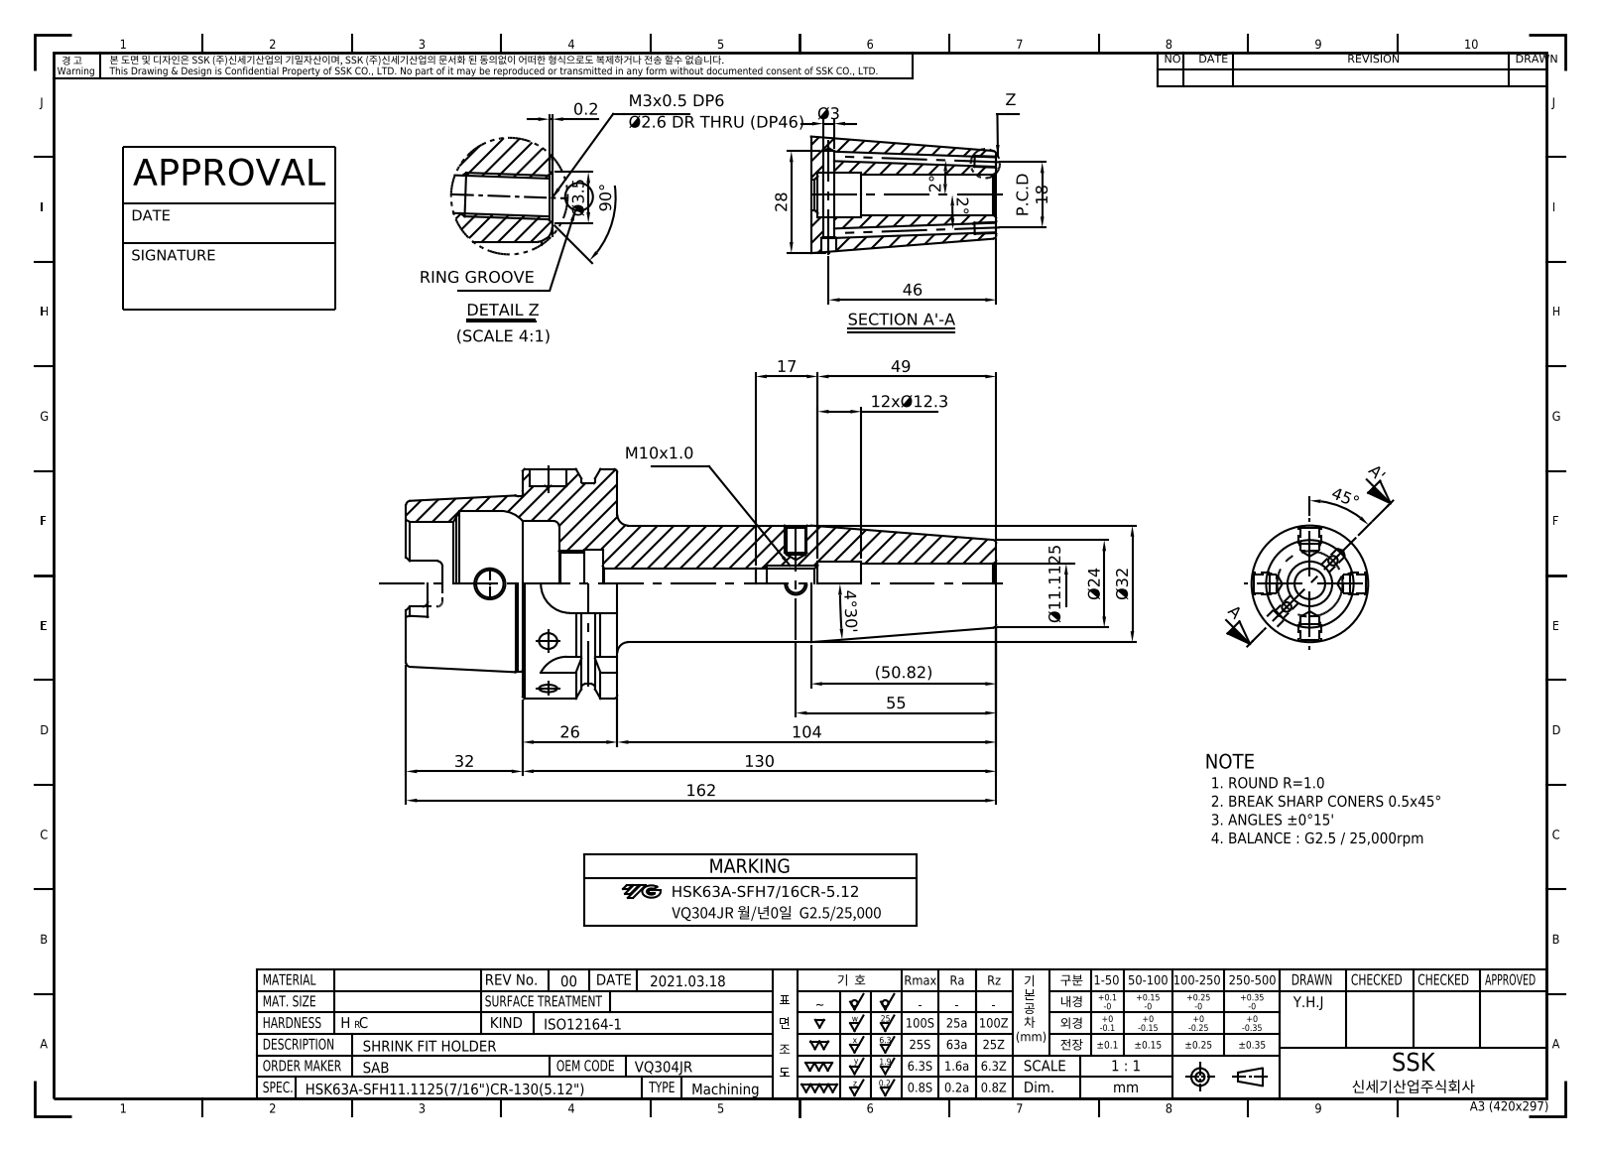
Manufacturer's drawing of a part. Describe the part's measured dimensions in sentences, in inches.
The part is named "LO-HSK63A-SFH11.1125CR-130". Its 3-D file was written by "Autodesk Inventor 2022 (AUTOMOTIVE_DESIGN)". It is 1 solid with 121 faces: 42 planar, 36 cylindrical and 43 other. Overall it measures 6.378 by 2.48 by 2.48 inches. Its volume is 8.988 cubic inches and its surface area 55.14 square inches. Round holes: 2 of diameter 0.097, 1 of diameter 0.295, 1 of diameter 0.331, 1 of diameter 0.351, 1 of diameter 0.394, 1 of diameter 0.437, 1 of diameter 0.484, 1 of diameter 0.666, 1 of diameter 0.748, 1 of diameter 1.339, 1 of diameter 1.575. Round bosses or shafts: 1 of diameter 2.48, 1 of diameter 2.165, 1 of diameter 1.891, 1 of diameter 1.26. Partial cylindrical surfaces (rounded edges, fillets, slot ends): 6 of radius 0.059, 4 of radius 0.113, 4 of radius 0.315. The main face-to-face distances are 1.024, 0.394, 0.63, 1.26, 1.654, 2.283, 2.087, 0.866, 0.157, 0.472.
